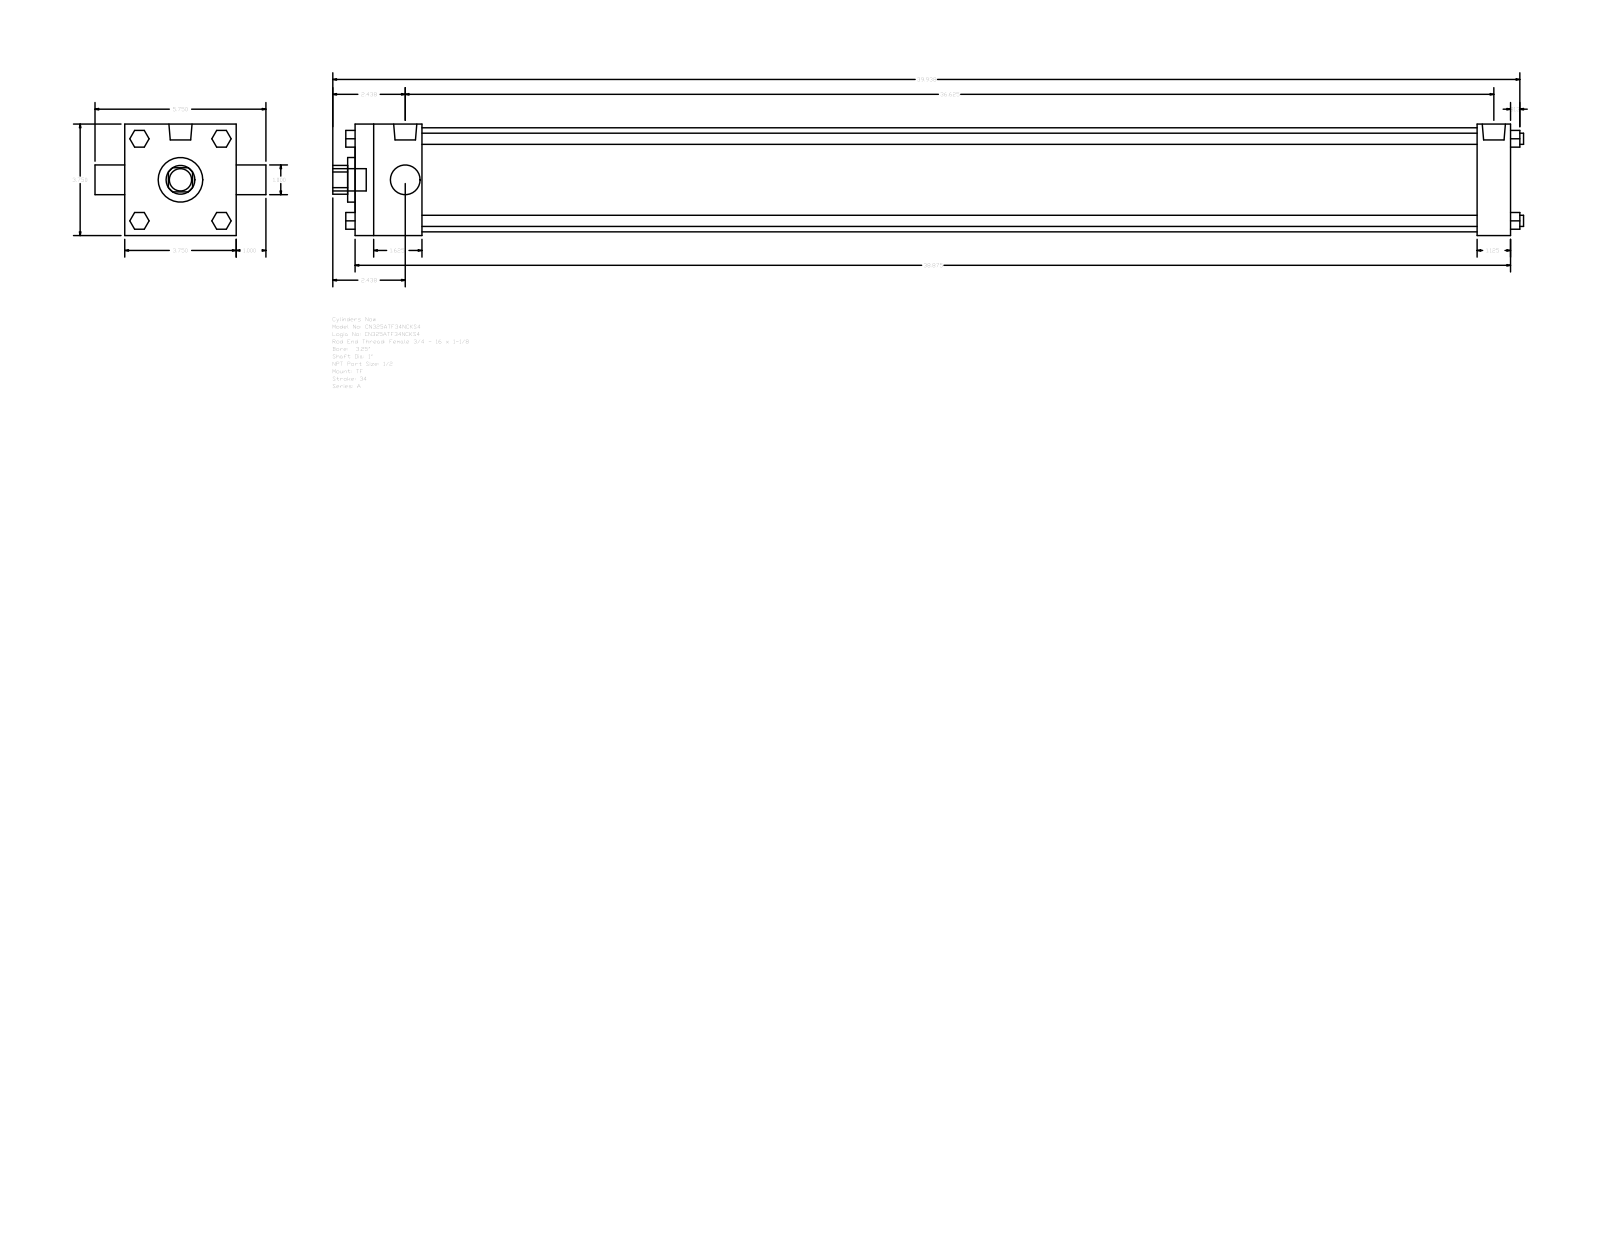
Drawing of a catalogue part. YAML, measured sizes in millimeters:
part_name: "A_TF__0325_1"
step_written_by: "GSSL Pune (CONFIG_CONTROL_DESIGN)"
units: millimeters
bodies: {solids: 0, faces: 120, planar: 92, cylindrical: 28, other: 0}
overall_size: [1017.59, 146.05, 95.25]
round_holes:
  - {diameter: 25.4, count: 2}
  - {diameter: 38.1, count: 1}
  - {diameter: 88.9, count: 1}
round_bosses_or_shafts:
  - {diameter: 9.53, count: 4}
  - {diameter: 8.73, count: 3}
  - {diameter: 19.77, count: 2}
  - {diameter: 19.05, count: 1}
partial_cylinders:
  - {radius: 12.29, count: 1}
face_to_face_distances: [95.24, 987.43, 57.15, 958.85, 901.7, 930.28, 28.58, 14.28, 35.05, 60.71]
